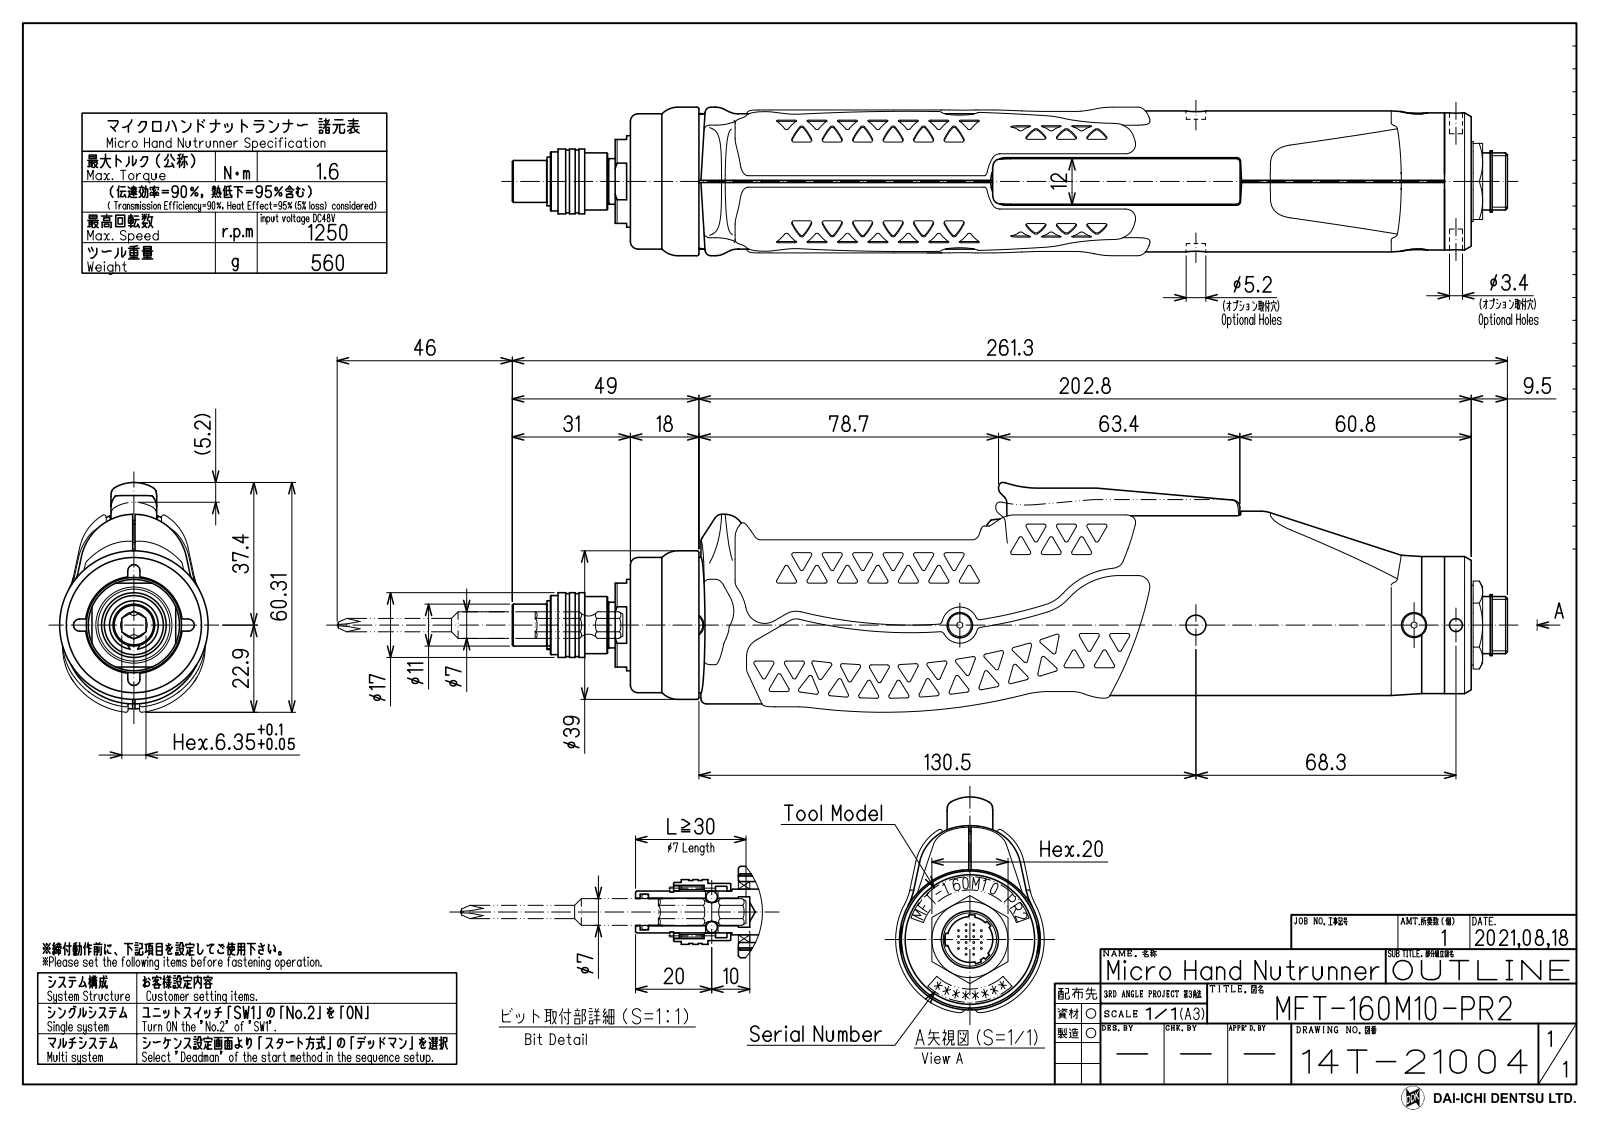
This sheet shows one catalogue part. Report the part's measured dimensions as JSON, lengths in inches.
{"part_name": "14T-21032_MFT-240M10-PR2(OUTLINE)_20211110-01", "step_written_by": "Autodesk Inventor 2021 (AUTOMOTIVE_DESIGN)", "units": "inches", "bodies": {"solids": 4, "faces": 2287, "planar": 707, "cylindrical": 706, "other": 874}, "overall_size": [10.287, 2.374, 1.535], "volume_in3": 17.38, "surface_area_in2": 75.58, "round_holes": [[0.118, 2], [0.126, 1], [0.134, 1], [0.276, 1], [0.315, 1], [0.37, 1], [0.531, 1], [0.551, 1], [0.583, 1], [1.004, 1], [1.276, 1], [1.315, 1]], "round_bosses_or_shafts": [[0.02, 20], [0.236, 3], [1.535, 1], [1.417, 1], [1.402, 1], [1.398, 1], [1.26, 1], [1.181, 1]], "partial_cylinders_radius": [[0.02, 144], [0.039, 57], [0.012, 24], [0.024, 18], [0.118, 13], [0.008, 10], [0.047, 7], [0.079, 7]], "face_to_face_distances": [0.039, 0.248, 0.224, 0.059, 0.413, 0.165, 0.189, 0.118, 0.472, 0.492], "hole_center_spacings": [5.524, 8.161]}
